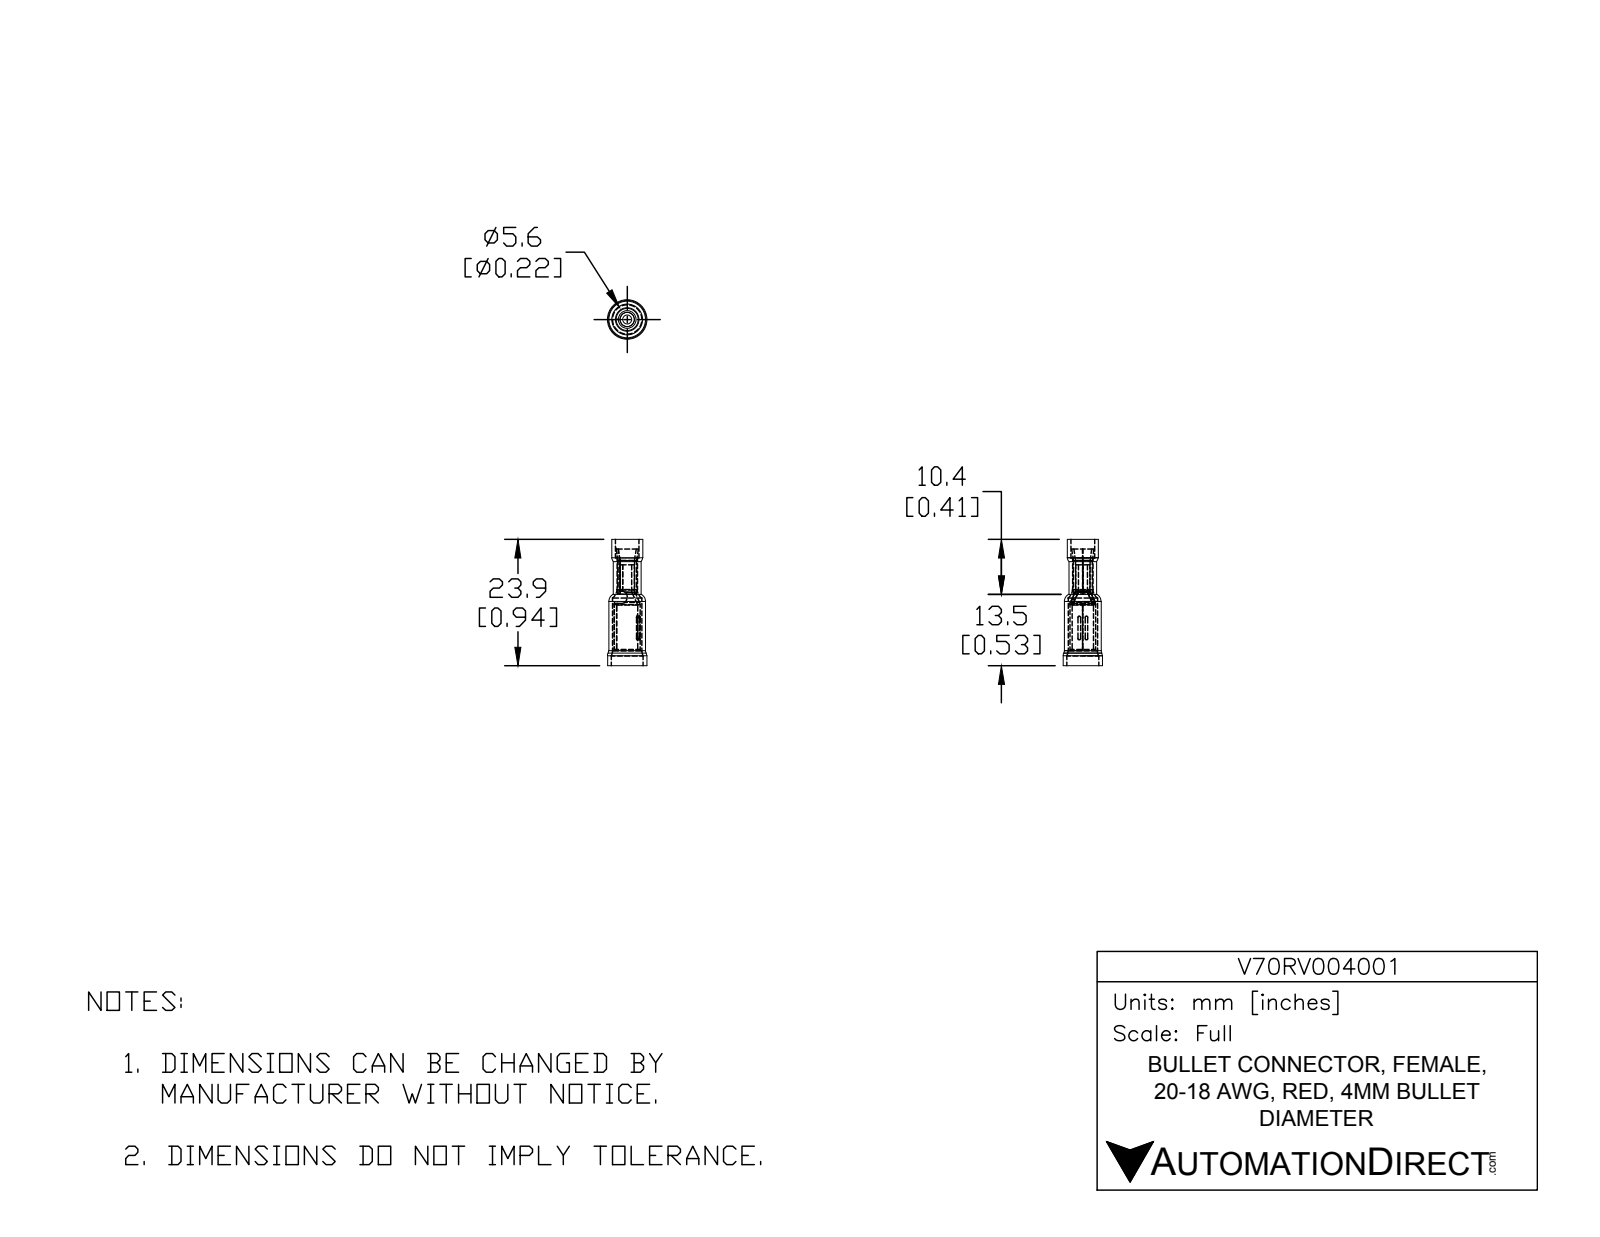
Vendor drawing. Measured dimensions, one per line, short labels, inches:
name: V70RV004001
written by: SolidWorks 2017 (AUTOMOTIVE_DESIGN)
unit: in
bodies: 3 solids, 89 faces (23 planar, 40 cylindrical, 26 other)
size: 0.941 × 0.293 × 0.293
volume: 0.025 in³; area: 2.243 in²
holes: 1× ⌀0.067, 1× ⌀0.108, 1× ⌀0.152, 1× ⌀0.157, 1× ⌀0.176, 1× ⌀0.219, 1× ⌀0.238
bosses: 1× ⌀0.293, 1× ⌀0.274, 1× ⌀0.231, 1× ⌀0.207, 1× ⌀0.193, 1× ⌀0.14, 1× ⌀0.106
rounds: 4× R0.01, 2× R0.039
face distances: 0.941, 0.071, 0.406, 0.122, 0.819, 0.87, 0.748, 0.02, 0.037, 0.535
